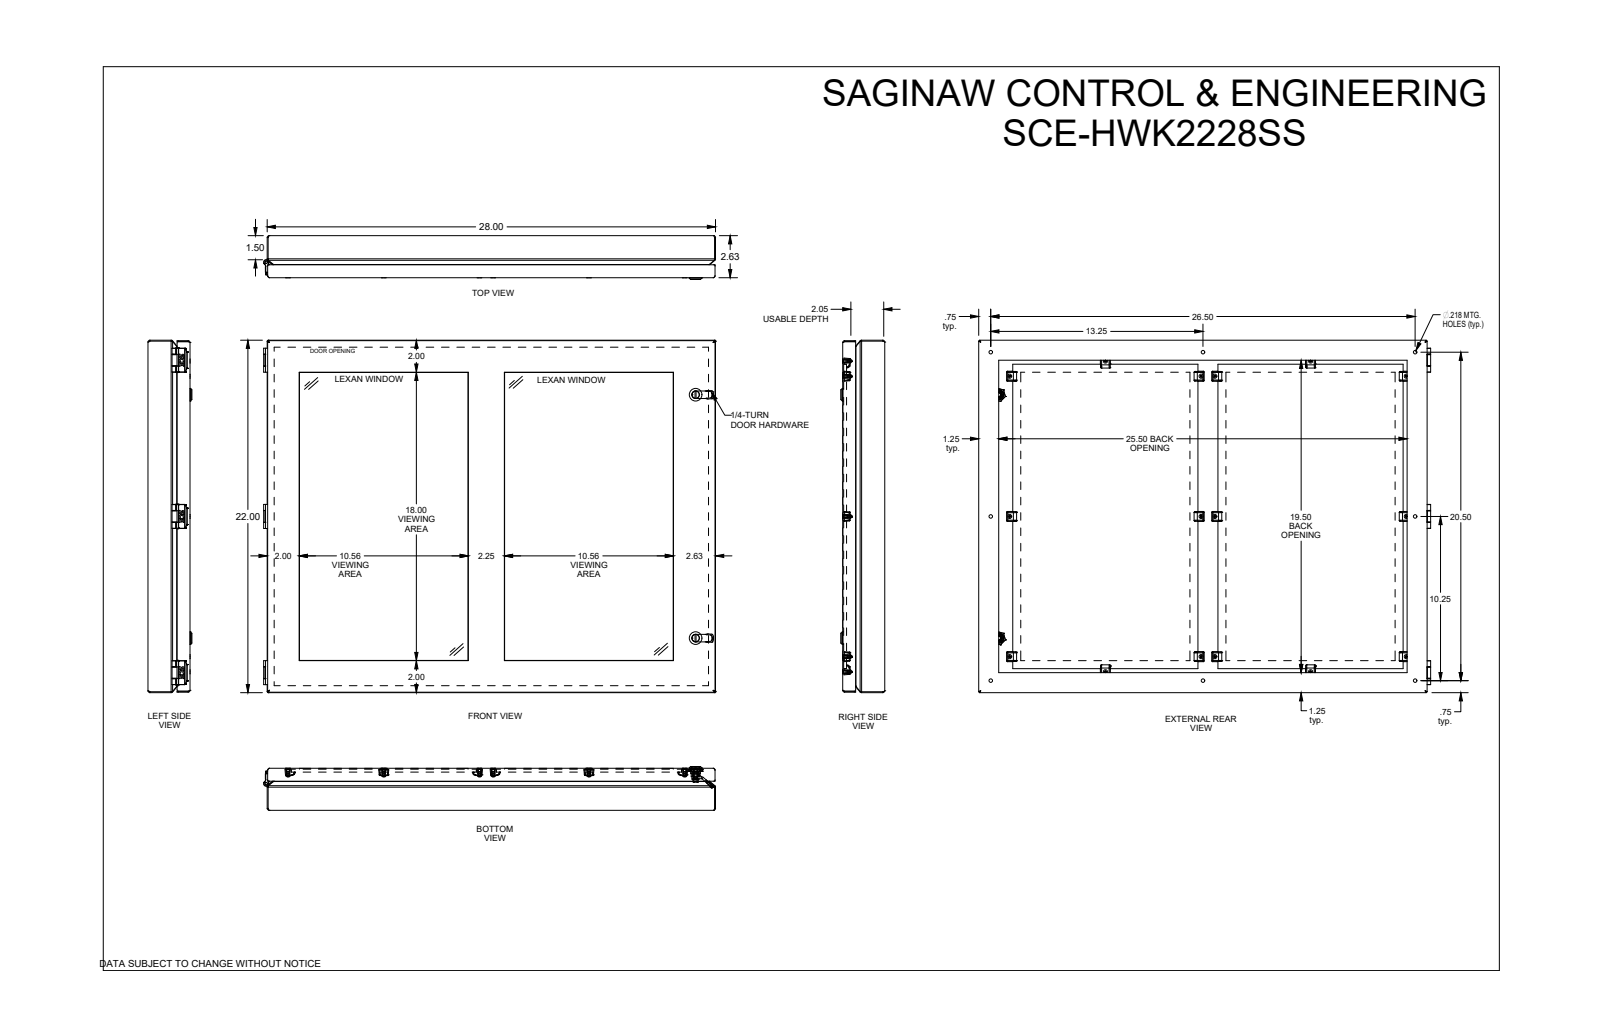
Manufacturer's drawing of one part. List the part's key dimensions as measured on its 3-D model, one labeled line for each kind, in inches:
Part name (STEP PRODUCT): SCE-HWK2228
STEP written by: SolidWorks 2021 (AUTOMOTIVE_DESIGN)
Units: inches
Bodies: 84 solids, 3389 faces (1422 planar, 939 cylindrical, 1028 other)
Overall size (bounding box): 28.22 × 22.06 × 2.733
Volume: 167.6 in³ · Surface area: 3 060 in²
Round holes (diameter × count): ⌀0.138 ×16, ⌀0.156 ×16, ⌀0.213 ×16, ⌀0.218 ×8, ⌀0.164 ×3, ⌀0.17 ×3, ⌀0.174 ×3, ⌀0.266 ×3, ⌀0.338 ×3, ⌀0.2 ×2, ⌀0.239 ×2, ⌀0.254 ×2
Round bosses / shafts (diameter × count): ⌀0.262 ×16, ⌀0.212 ×16, ⌀0.479 ×3, ⌀0.26 ×3, ⌀0.15 ×3, ⌀0.788 ×2, ⌀0.548 ×2, ⌀0.46 ×2
Partial cylindrical surfaces — rounded edges, fillets, slot ends (radius × count): R0.106 ×99, R0.05 ×64, R0.005 ×54, R0.008 ×48, R0.02 ×44, R0.025 ×18, R0.01 ×16, R0.06 ×16
Main face-to-face distances: 0.06, 0.181, 0.241, 0.236, 0.055, 0.059, 0.09, 0.031, 2.385, 2.566
Hole centre spacings: 6.054, 8.75, 11.393, 12.812, 14.817, 15.515, 19.392, 11.957
